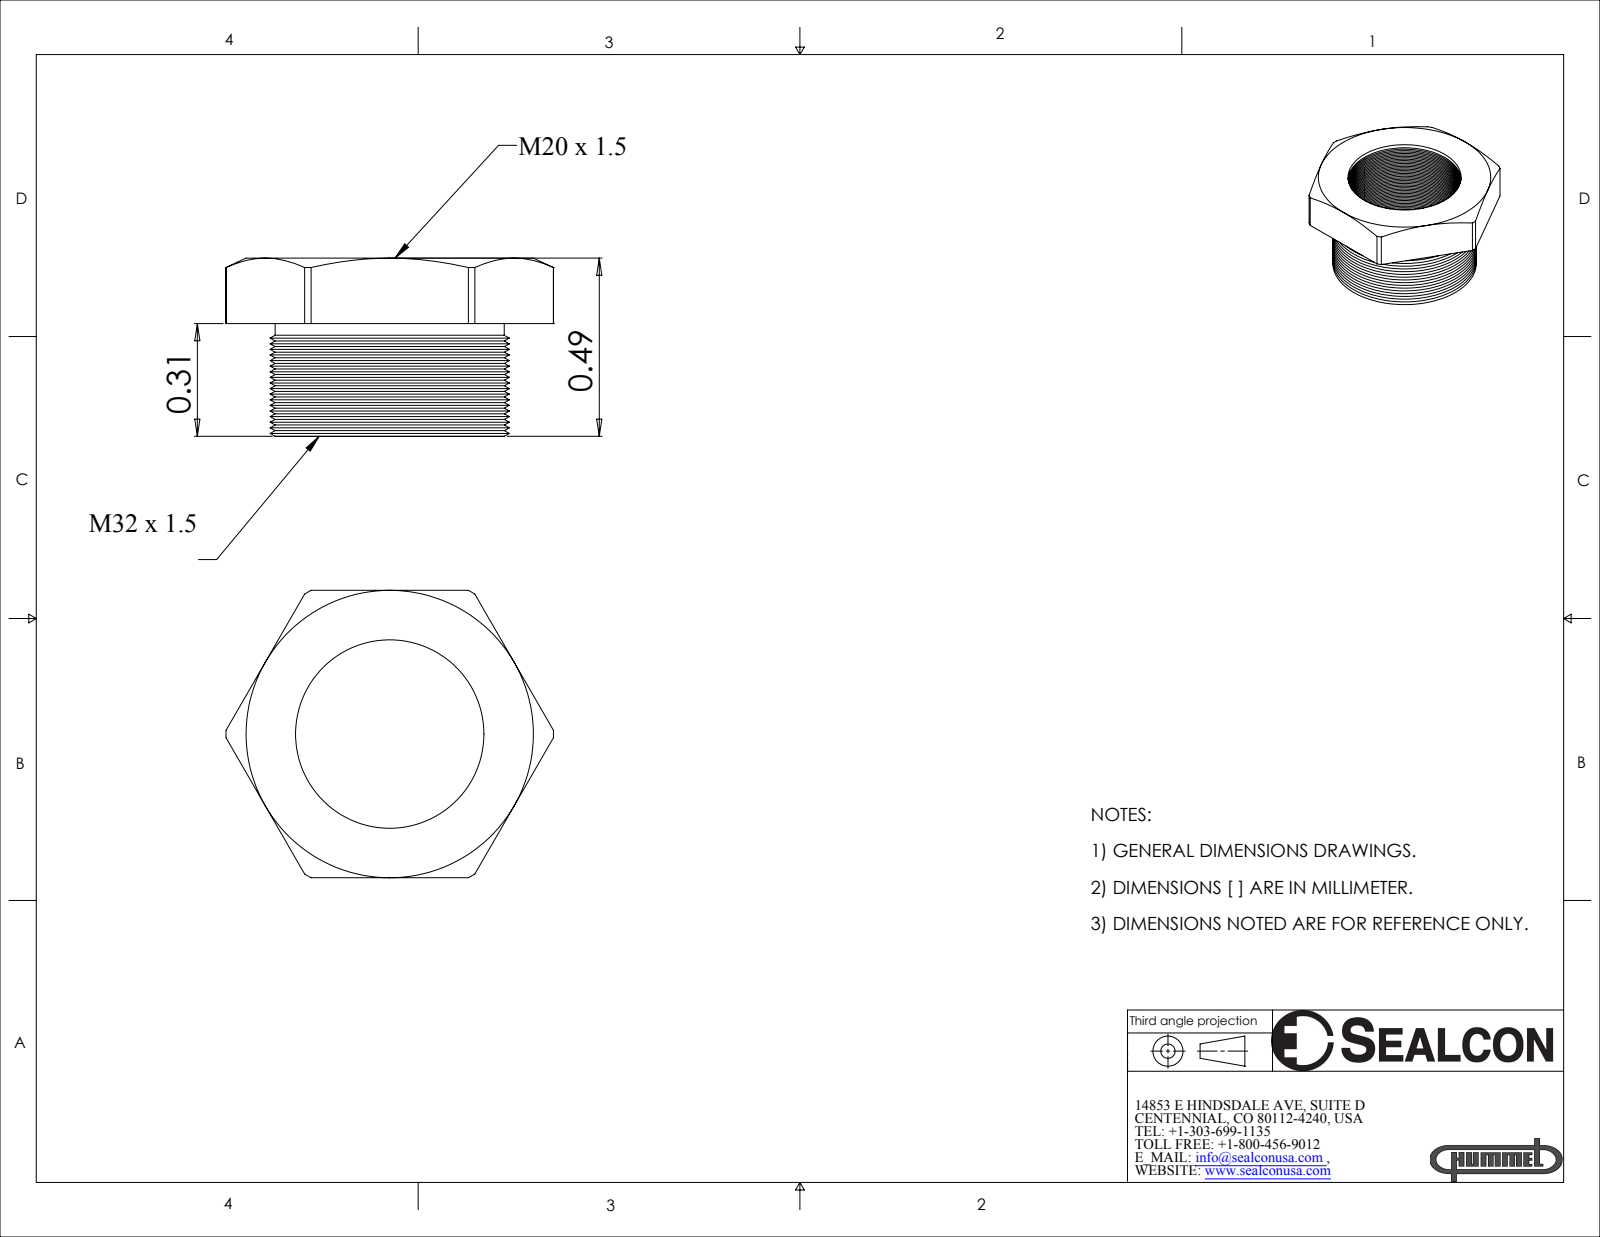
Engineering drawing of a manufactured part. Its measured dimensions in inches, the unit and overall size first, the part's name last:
Units: inches
Overall size (bounding box): 0.901 × 0.79 × 0.49
Round holes (diameter × count): ⌀0.518 ×1
Round bosses / shafts (diameter × count): ⌀0.63 ×1
Partial cylindrical surfaces — rounded edges, fillets, slot ends (radius × count): R0.45 ×1
Main face-to-face distances: 0.18, 0.79, 0.31, 0.49
Volume: 0.092 in³ · Surface area: 3.933 in²
Bodies: 1 solid, 281 faces (9 planar, 73 cylindrical, 199 other)
Part name (STEP PRODUCT): RM-3220-SS
STEP written by: SolidWorks 2008 (CONFIG_CONTROL_DESIGN)
